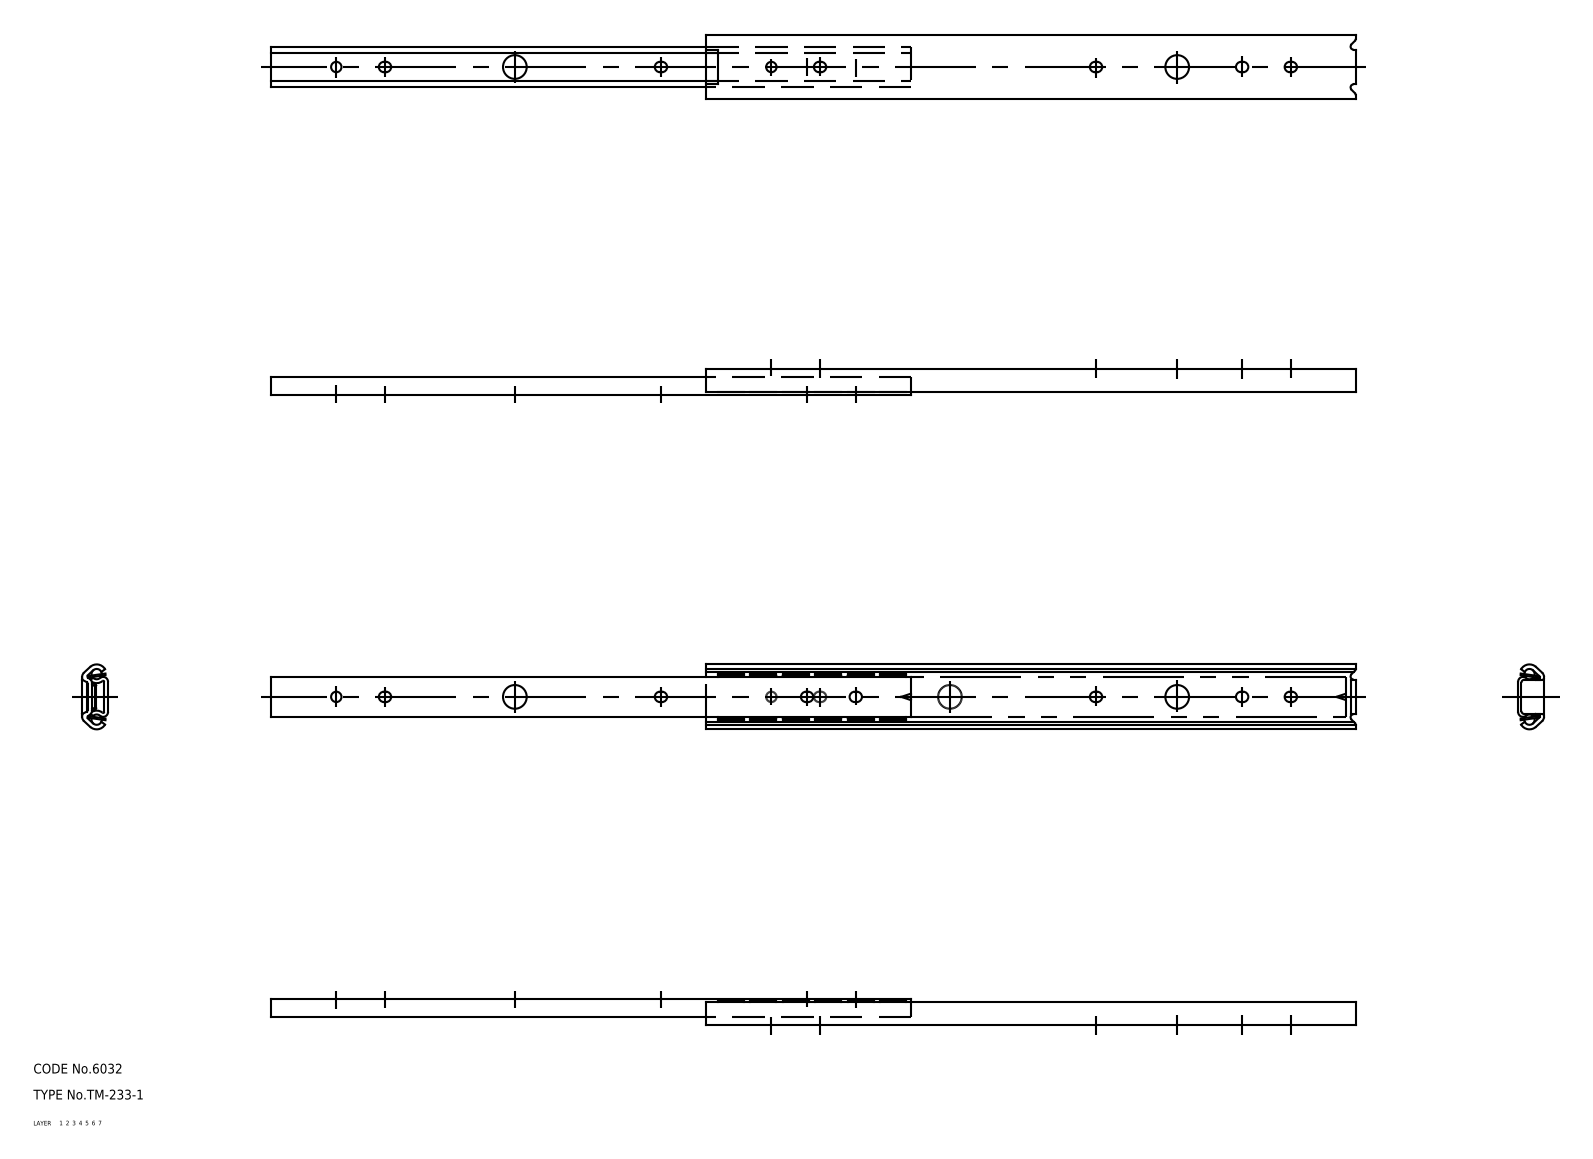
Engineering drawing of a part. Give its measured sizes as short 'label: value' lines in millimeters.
name: ball; retainer; member_B; member_A (+1 more)
written by: CADfix (AUTOMOTIVE_DESIGN)
unit: mm
bodies: 15 solids, 256 faces (0 planar, 0 cylindrical, 256 other)
size: 334 × 20 × 8
volume: 12 959 mm³; area: 23 062 mm²
